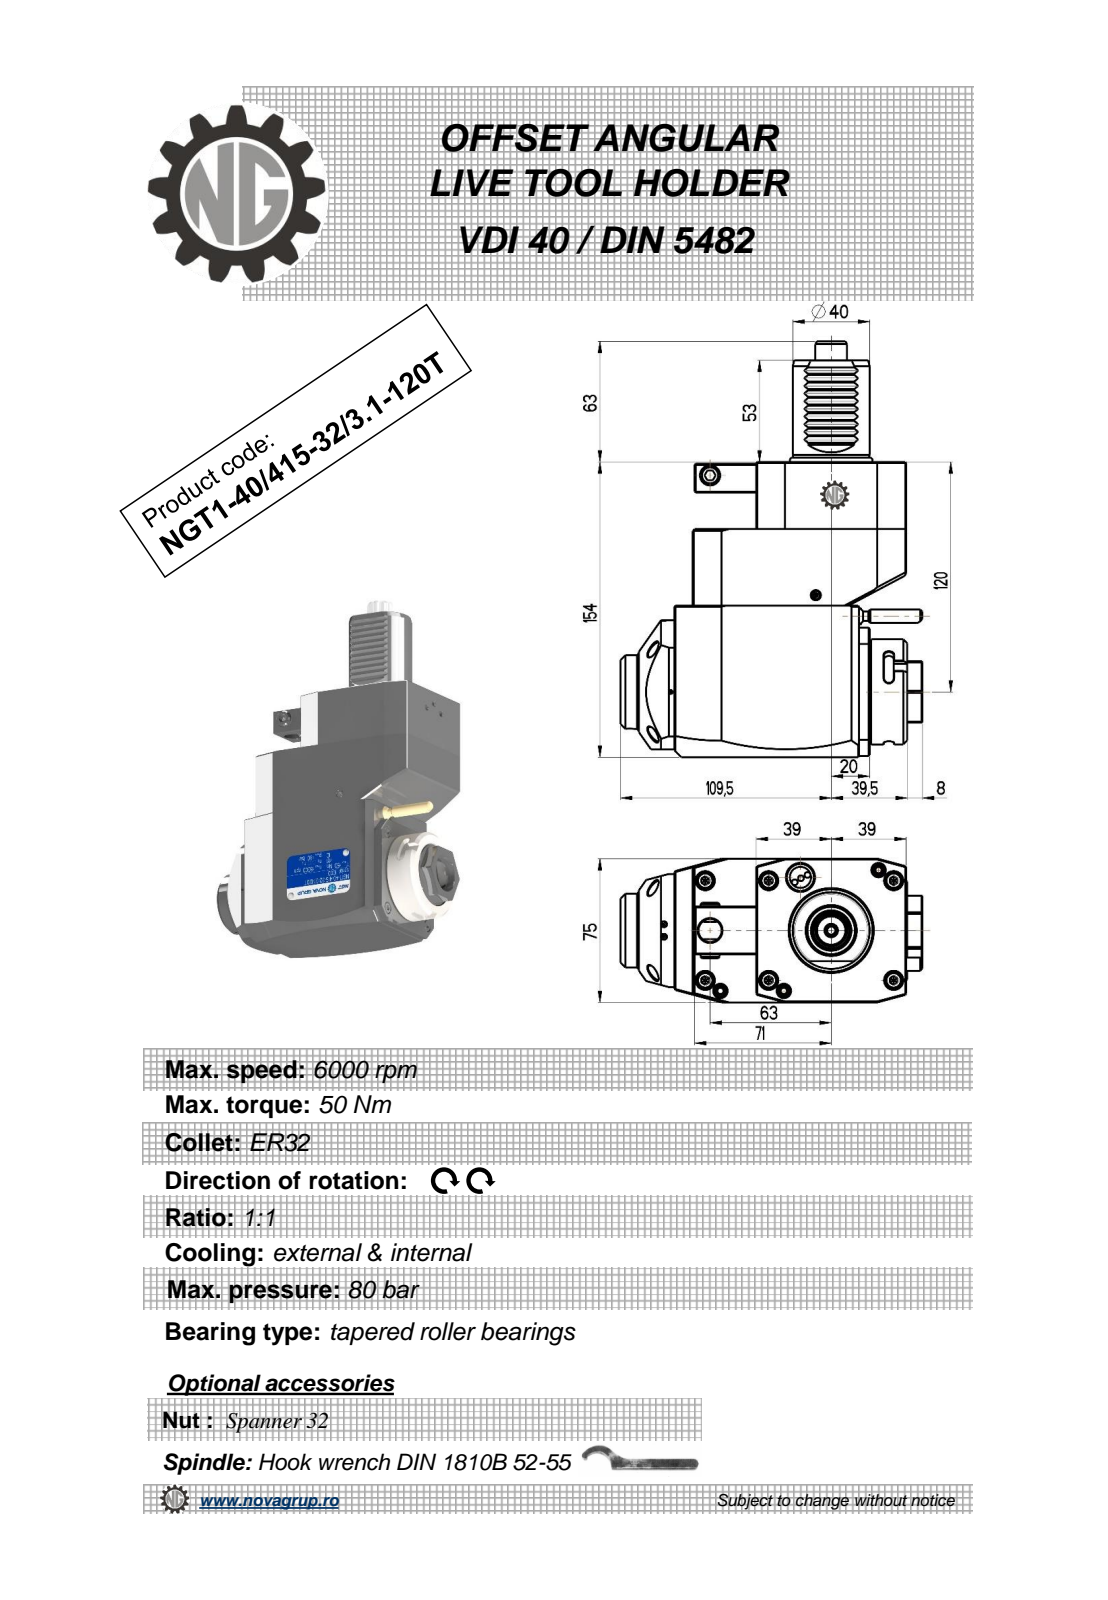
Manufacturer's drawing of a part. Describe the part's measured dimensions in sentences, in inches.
The part is named "NGT1_40_415_32_3_1_120T". Its 3-D file was written by "PRO/ENGINEER BY PARAMETRIC TECHNOLOGY CORPORATION, 2010280 (CONFIG_CONTROL_DESIGN)". It is 1 solid with 377 faces: 185 planar, 103 cylindrical and 89 other. Overall it measures 8.543 by 6.181 by 2.953 inches. Its volume is 77.74 cubic inches and its surface area 138.5 square inches. Round holes: 1 of diameter 0.098, 1 of diameter 0.118, 1 of diameter 0.165, 1 of diameter 0.209, 1 of diameter 0.374, 1 of diameter 0.472, 1 of diameter 0.906. Round bosses or shafts: 2 of diameter 0.353, 1 of diameter 2.165, 1 of diameter 1.89, 1 of diameter 1.575, 1 of diameter 1.516, 1 of diameter 0.394, 1 of diameter 0.276, 1 of diameter 0.197. Partial cylindrical surfaces (rounded edges, fillets, slot ends): 18 of radius 0.119, 10 of radius 0.012, 6 of radius 0.098, 2 of radius 7.087, 1 of radius 0.02, 1 of radius 0.167, 1 of radius 0.266, 1 of radius 0.325. The main face-to-face distances are 2.953, 6.063, 0.748, 2.323, 4.37, 3.622, 1.378, 4.685, 1.299, 0.02. The hole center spacings are 1.701, 2.48, 2.956, 4.429.
